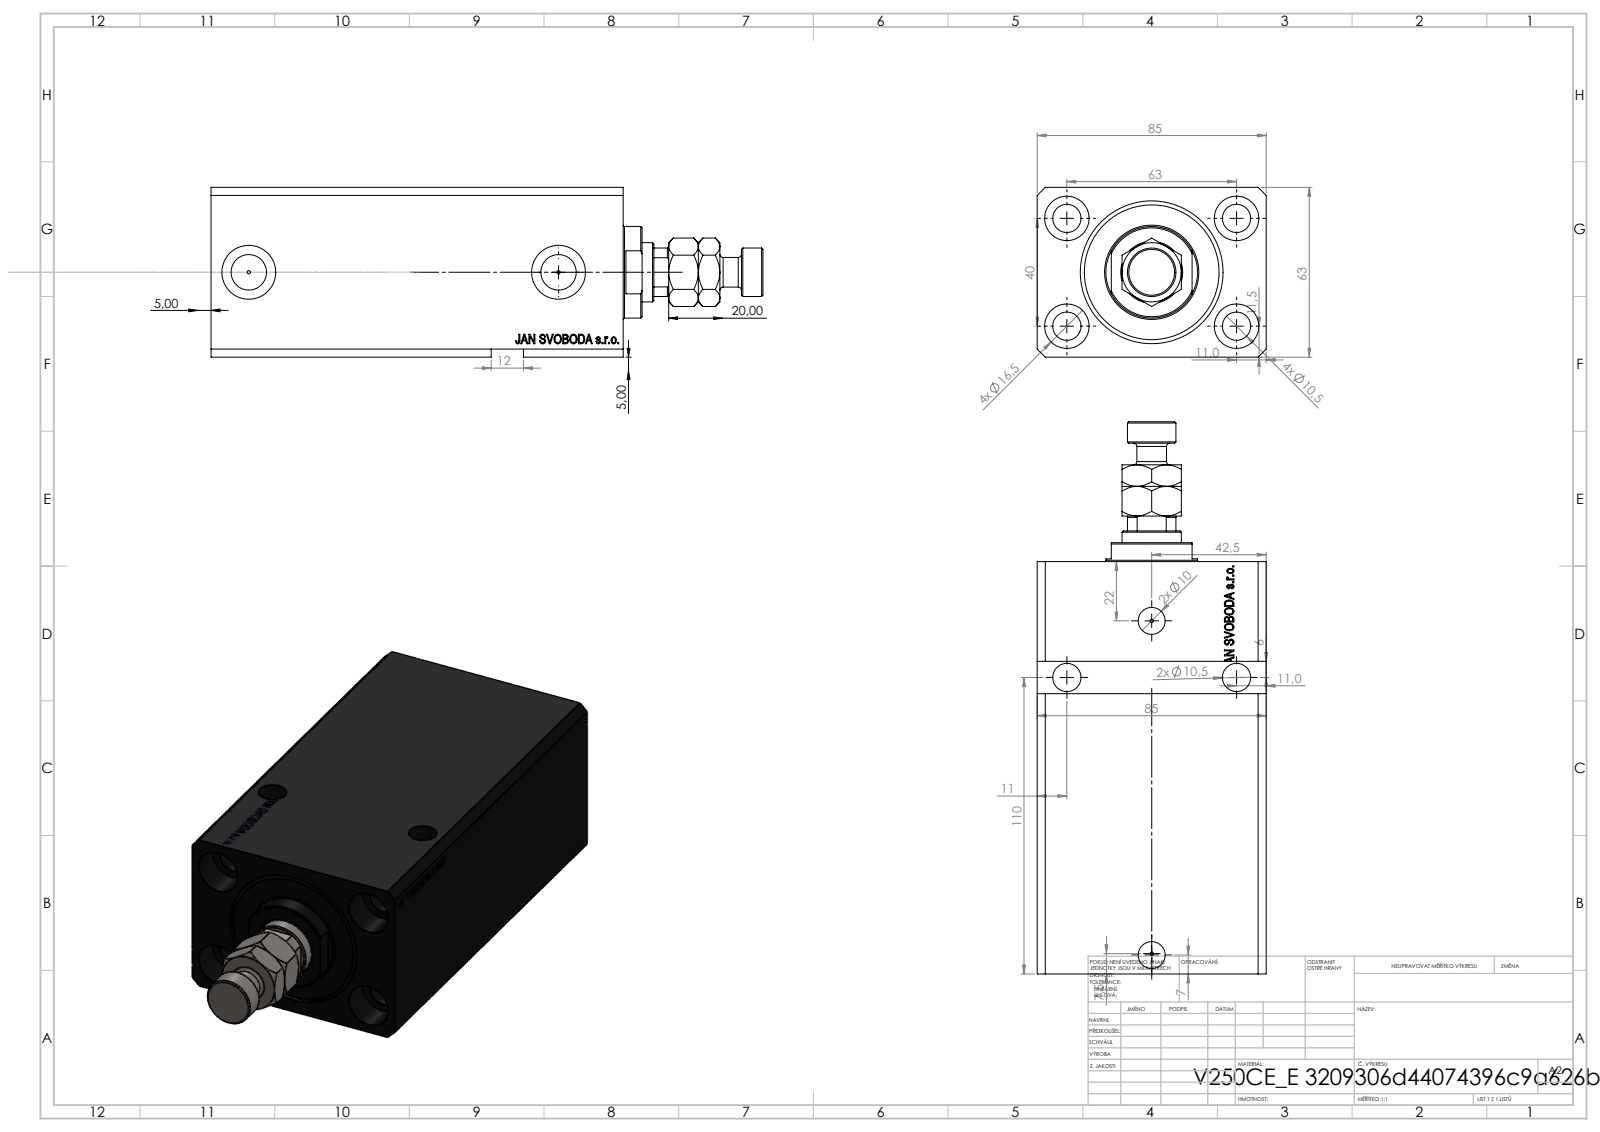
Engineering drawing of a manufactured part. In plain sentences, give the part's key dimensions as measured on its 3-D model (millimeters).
The part is named "MFA; V250CE_E_Body; V250CE_VC_E; V250CE_C_VCP". Its 3-D file was written by "SolidWorks 2019 (CONFIG_CONTROL_DESIGN)". It is 4 solids with 989 faces: 475 planar, 108 cylindrical and 406 other. Overall it measures 205 by 85 by 63 millimeters. Its volume is 676 886 cubic millimeters and its surface area 129 466 square millimeters. Round holes: 8 of diameter 10.5, 4 of diameter 1.25, 4 of diameter 16.5, 2 of diameter 10, 2 of diameter 13.16, 2 of diameter 20, 1 of diameter 12.5, 1 of diameter 22, 1 of diameter 40, 1 of diameter 53. Round bosses or shafts: 1 of diameter 34, 1 of diameter 18, 1 of diameter 11. Partial cylindrical surfaces (rounded edges, fillets, slot ends): 1 of radius 10.5. The main face-to-face distances are 63, 85, 17, 153, 136, 11.4, 124.6, 141.6, 56, 60. The hole center spacings are 37.31, 63, 37.86, 40, 41.8, 42.15, 74.63, 75.
